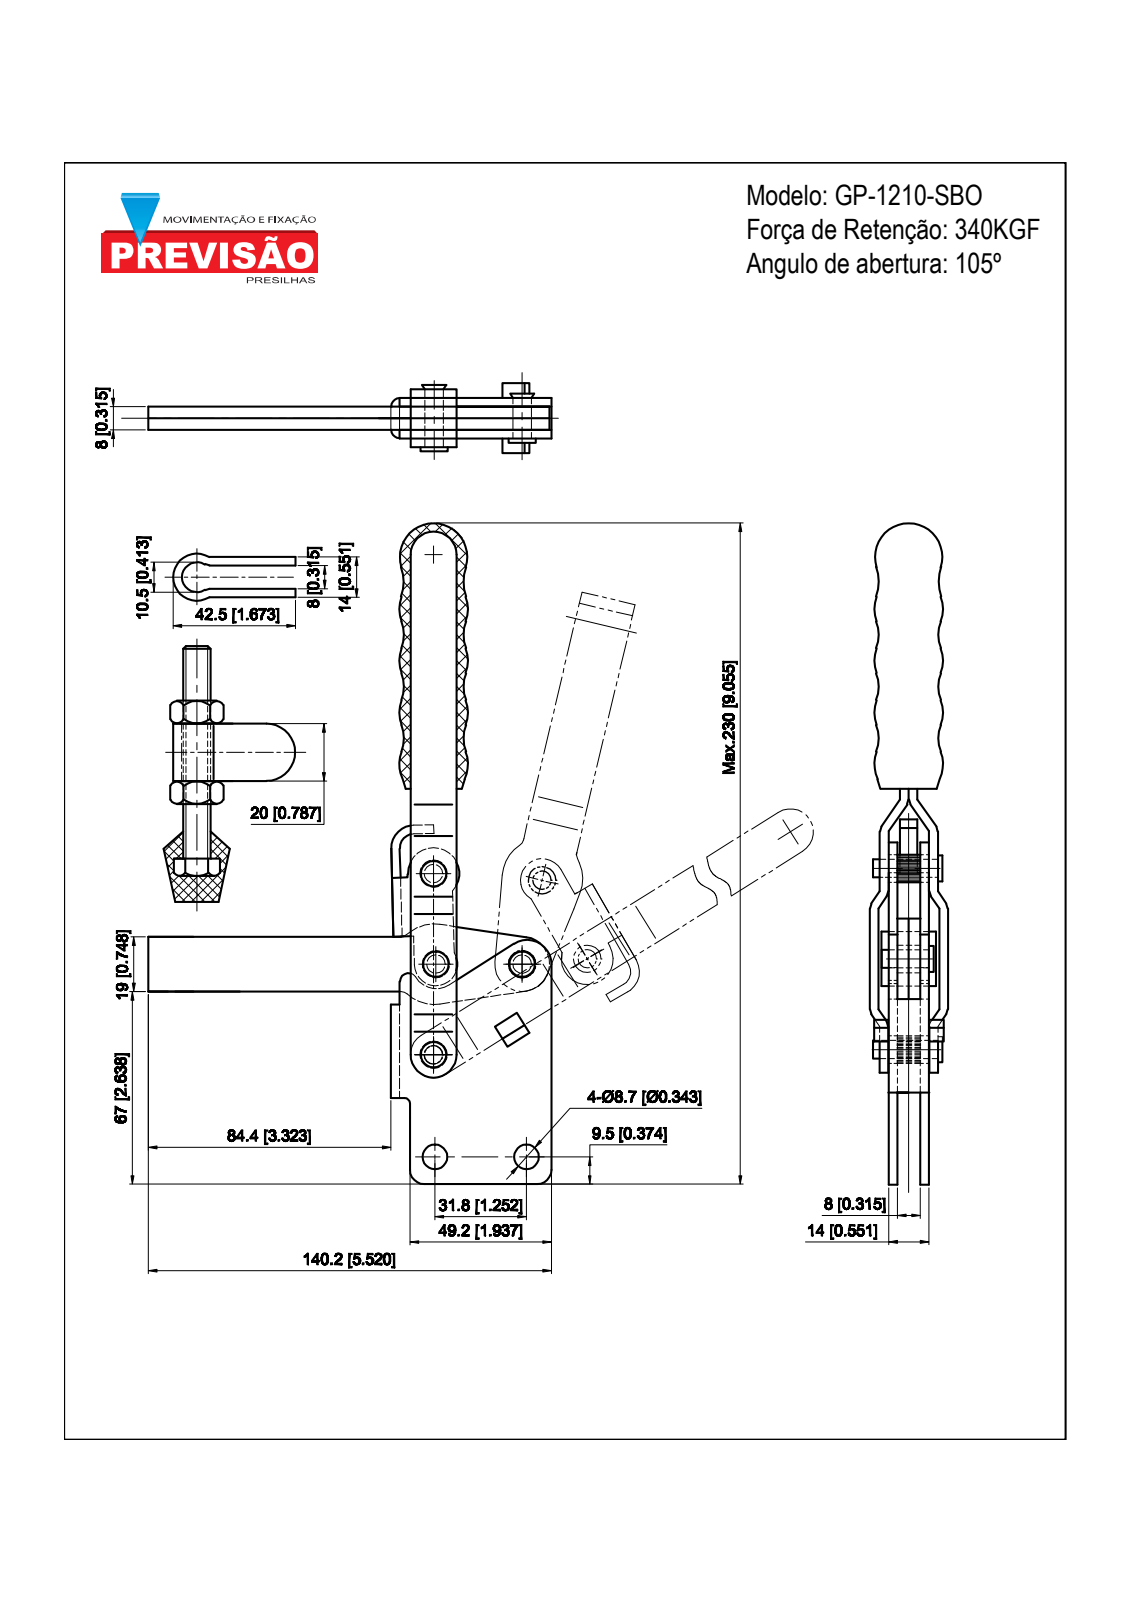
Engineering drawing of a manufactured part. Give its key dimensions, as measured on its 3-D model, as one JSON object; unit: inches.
{"part_name": "CH-FC-38312 SPINDLE SUPPLIED; CH-12265-07; CH-12265-03 STRAIGHT HANDLE; CH-12280 (+7 more)", "step_written_by": "SolidWorks 2015 (CONFIG_CONTROL_DESIGN)", "units": "inches", "bodies": {"solids": 18, "faces": 832, "planar": 282, "cylindrical": 236, "other": 314}, "overall_size": [8.934, 6.366, 1.063], "volume_in3": 6.961, "surface_area_in2": 112.1, "round_holes": [[0.374, 5], [0.252, 4], [0.343, 2], [0.115, 1], [0.546, 1]], "round_bosses_or_shafts": [[0.378, 4], [0.354, 4], [0.374, 1], [0.104, 1]], "partial_cylinders_radius": [[0.118, 25], [0.197, 4], [0.315, 4], [0.079, 2], [0.335, 2], [0.207, 1], [0.295, 1], [0.325, 1]], "face_to_face_distances": [0.118, 0.433, 0.315, 0.551, 0.276, 0.158, 0.276, 0.157, 0.275, 0.394], "hole_center_spacings": [1.181, 1.24, 1.241, 1.252, 1.407, 1.727, 1.735, 1.897]}
